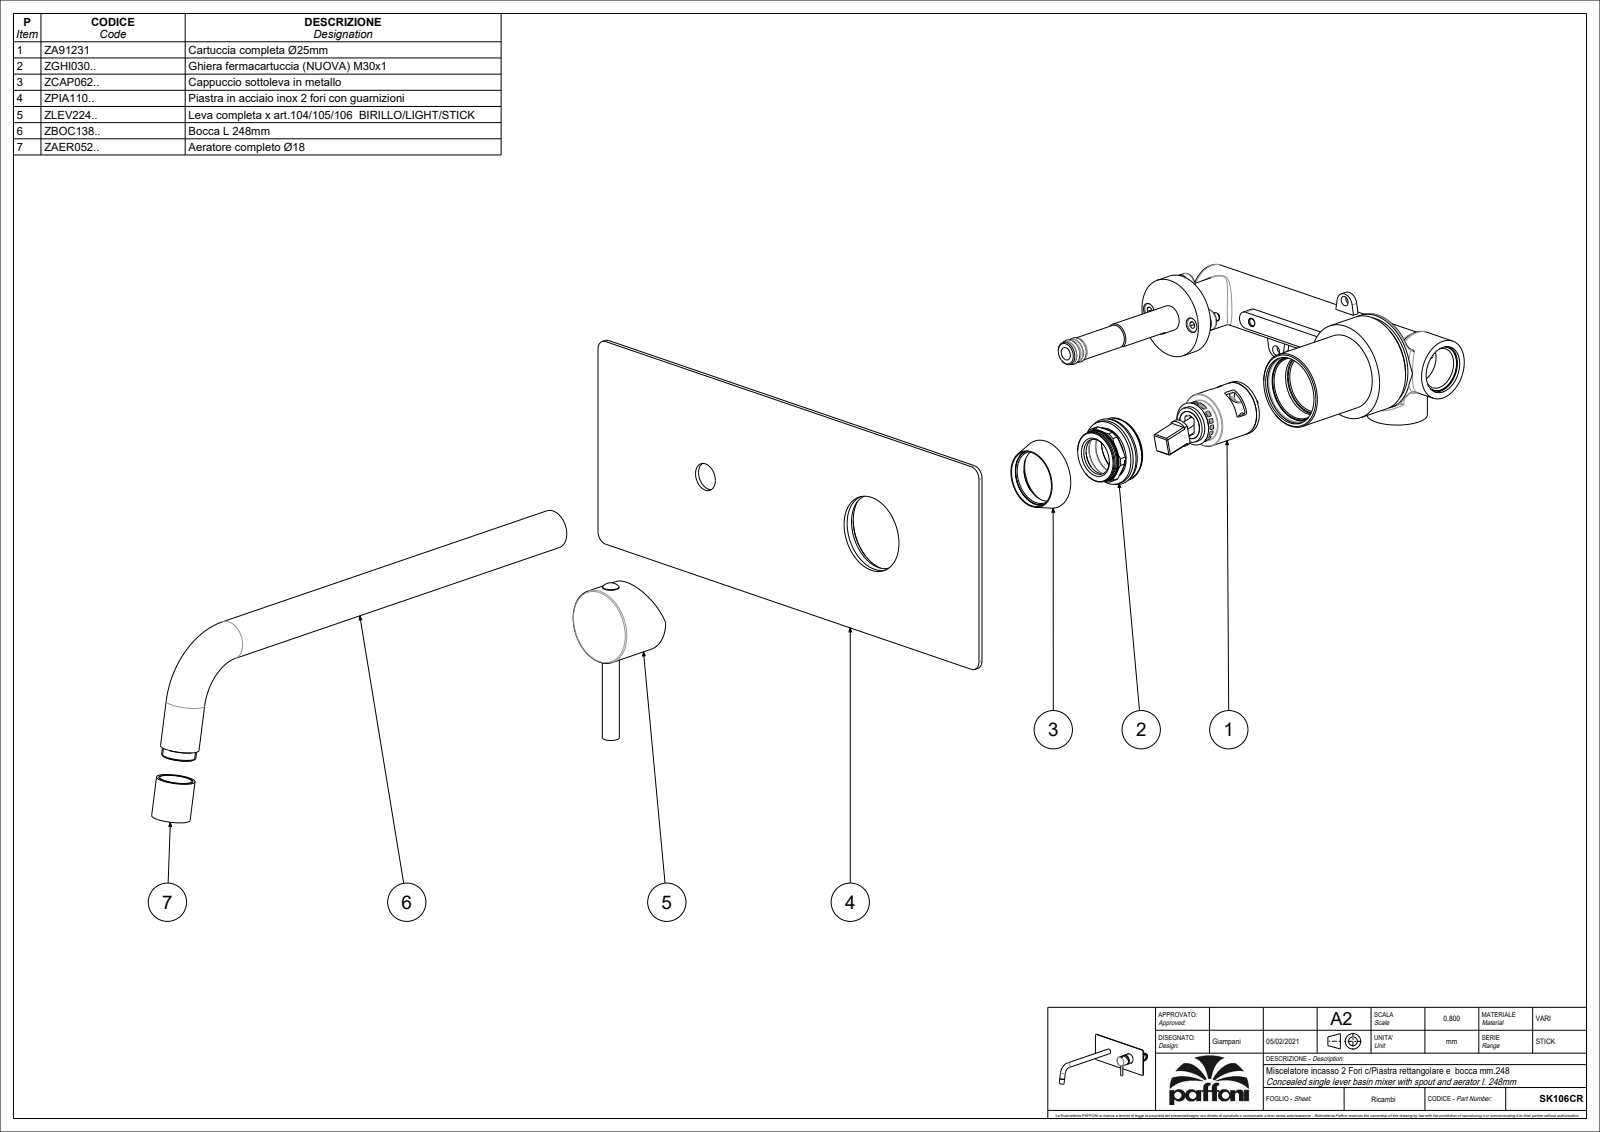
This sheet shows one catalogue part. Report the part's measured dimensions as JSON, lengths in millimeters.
{"part_name": "SK106CR", "step_written_by": "CREO PARAMETRIC BY PTC INC, 2020044 (CONFIG_CONTROL_DESIGN)", "units": "millimeters", "bodies": {"solids": 2, "faces": 953, "planar": 238, "cylindrical": 485, "other": 230}, "overall_size": [259.08, 250, 114.78], "volume_mm3": 127765, "surface_area_mm2": 103443, "round_holes": [[0.5, 51], [4.2, 2], [10, 2], [11, 2], [12, 2], [3, 1], [6, 1], [8.1, 1], [13, 1], [14, 1], [15, 1], [15.5, 1]], "round_bosses_or_shafts": [[18, 2], [5, 2], [35.2, 1], [35, 1], [30, 1], [27.7, 1], [25, 1], [23.8, 1]], "partial_cylinders_radius": [[0.5, 58], [1, 21], [5, 5], [2, 4], [3, 4], [3.5, 3], [1.5, 2], [5.9, 2]], "face_to_face_distances": [2, 6.5, 5.8, 16, 14, 100, 48.6, 46.6, 32.6, 0.7], "hole_center_spacings": [1.5, 3.35, 2.12, 4.74, 3, 4.24, 4.5, 6.71]}
